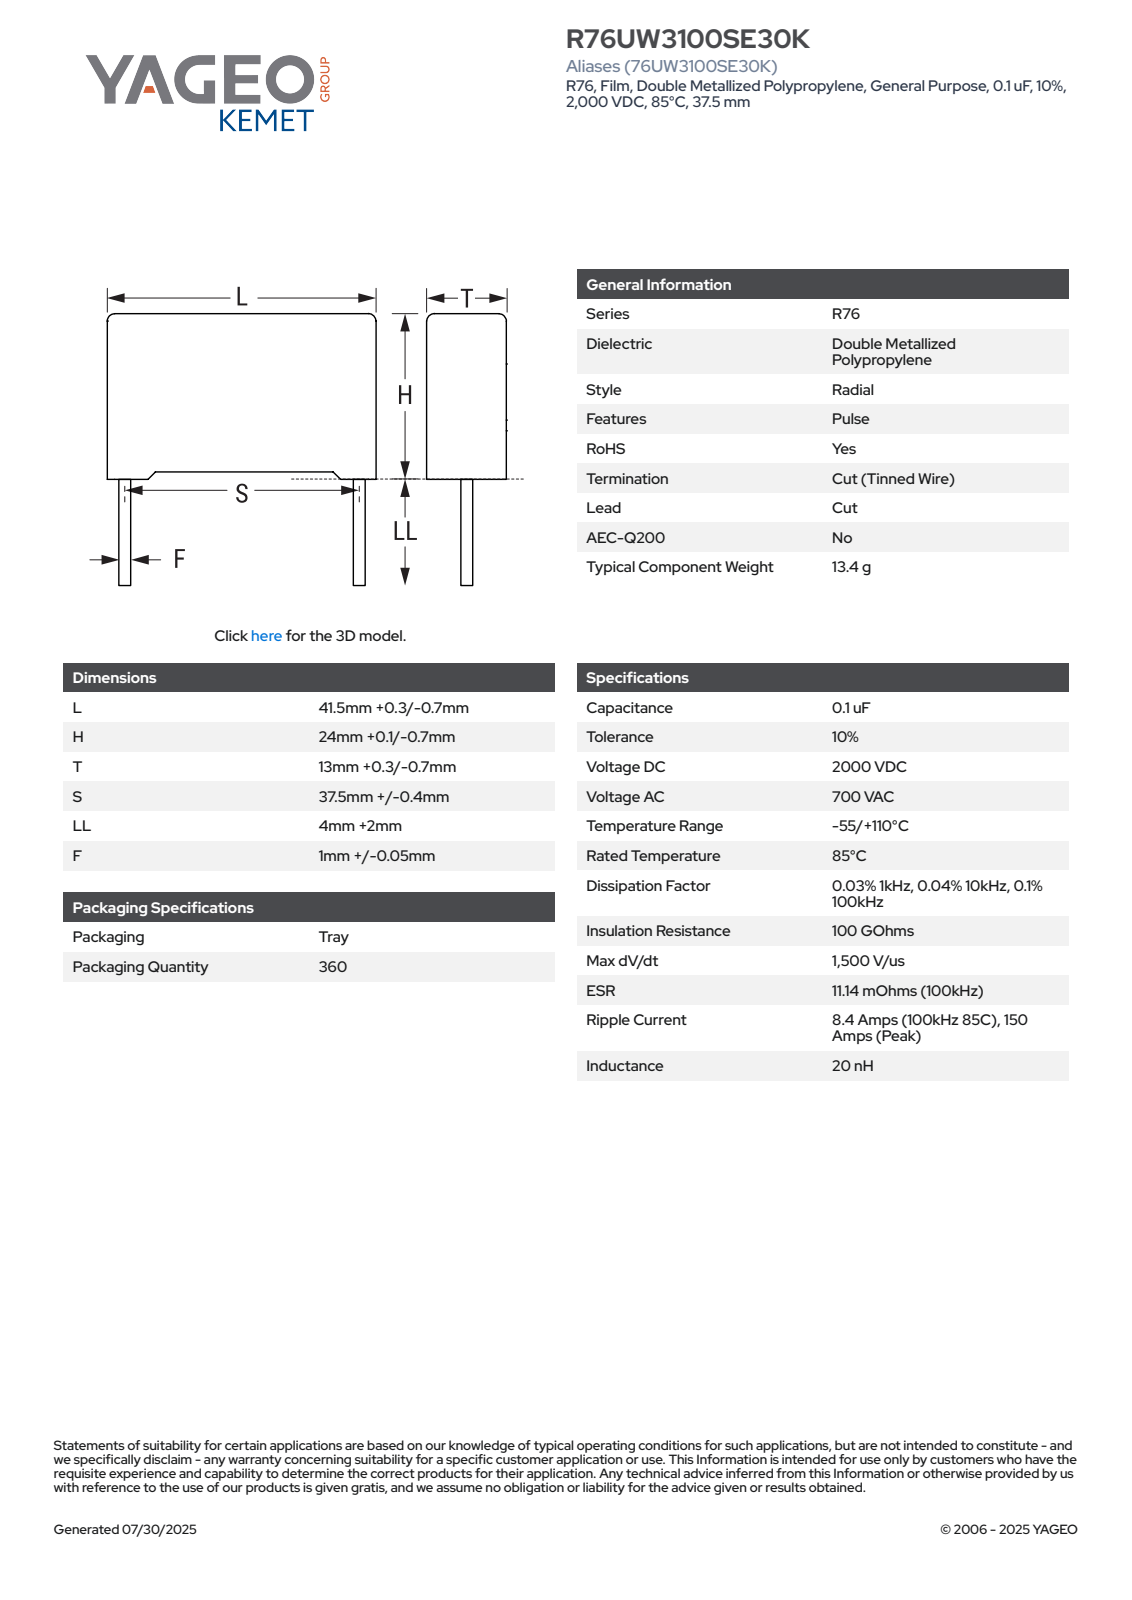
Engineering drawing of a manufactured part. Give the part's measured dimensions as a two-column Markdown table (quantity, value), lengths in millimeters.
| quantity | value |
| --- | --- |
| part name | CFR_RB2_41.5X24X13_L41.8H24.1T13.3S37.5LL6F1.05 |
| STEP written by | SolidWorks 2021 (AUTOMOTIVE_DESIGN) |
| units | millimeters |
| bodies | 4 solids, 85 faces (77 planar, 8 cylindrical, 0 other) |
| overall size | 41.8 × 30.1 × 13.3 |
| volume | 12 992 mm³ |
| surface area | 3 890 mm² |
| round bosses / shafts (diameter × count) | 1.05 × 2 |
| partial cylindrical surfaces (radius × count) | 0.5 × 4 |
| main face-to-face distances | 13.3, 23.27, 41.8, 23.35, 0.75, 0.83, 24.1, 13.31, 1.39, 40.41 |
